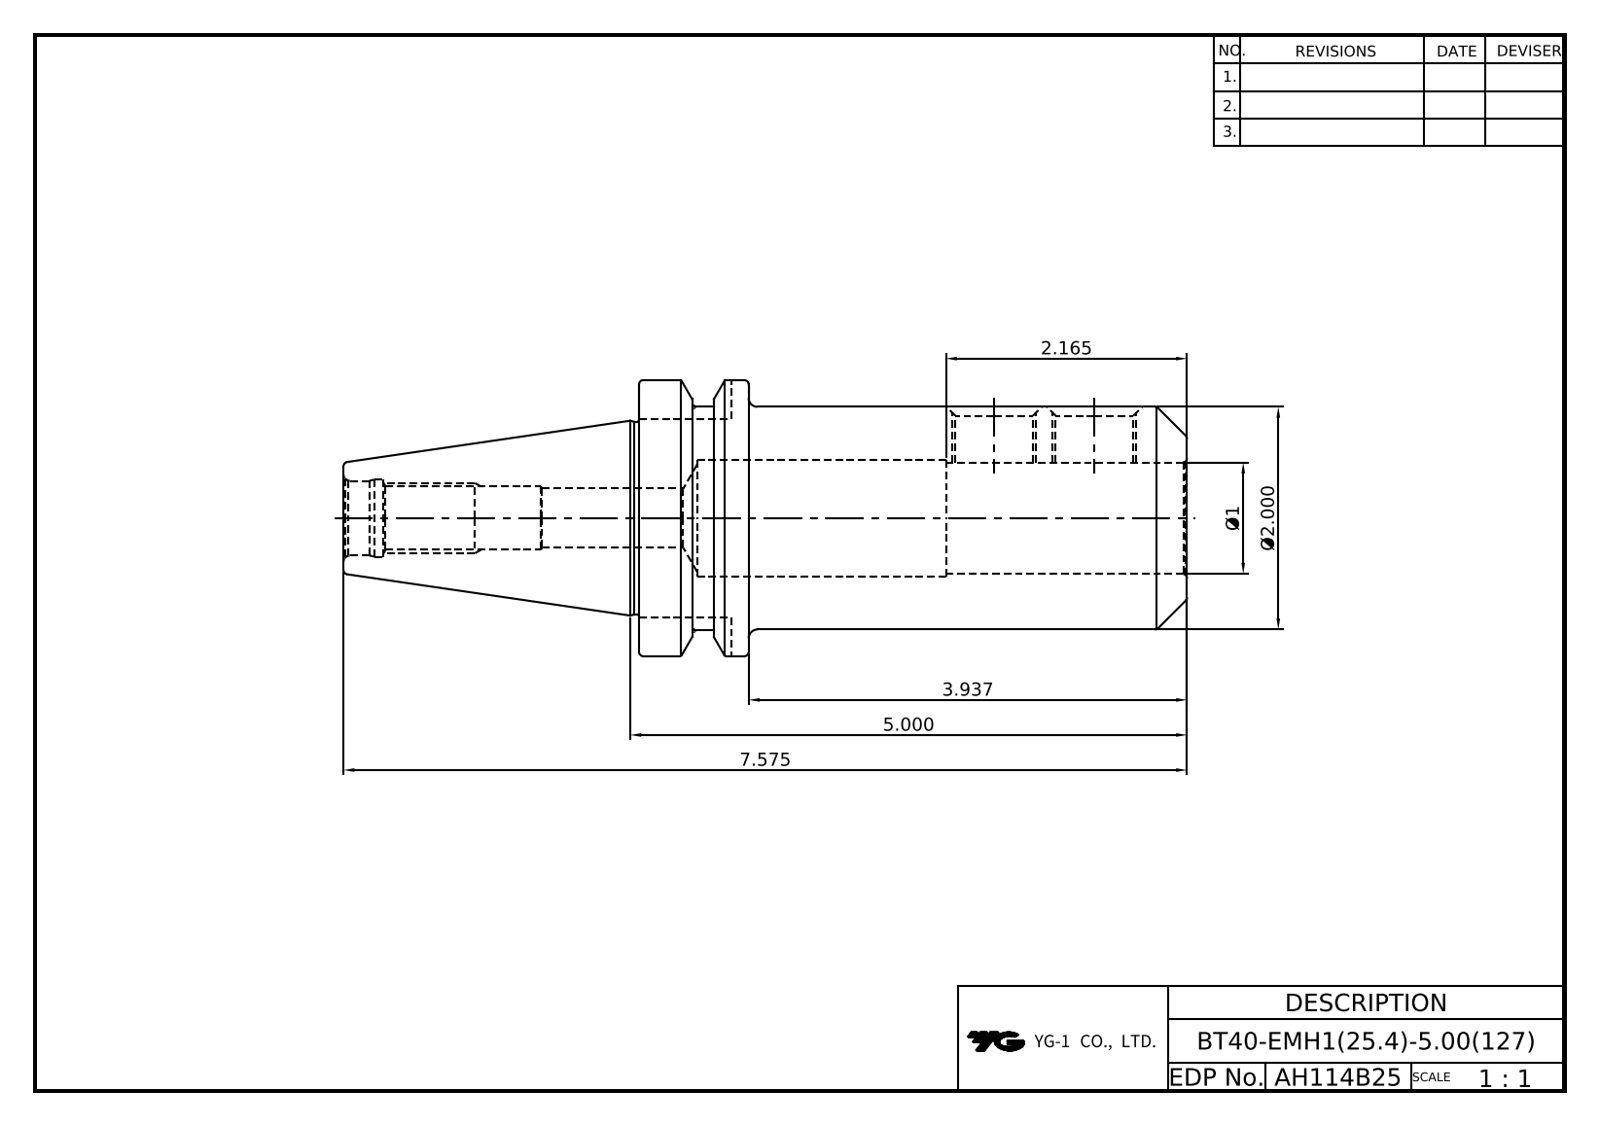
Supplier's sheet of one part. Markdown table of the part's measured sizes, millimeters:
| quantity | value |
| --- | --- |
| part name | LO-BT40-EMH25.4-127 |
| STEP written by | Autodesk Inventor 2022 (AUTOMOTIVE_DESIGN) |
| units | millimeters |
| bodies | 1 solid, 56 faces (17 planar, 17 cylindrical, 22 other) |
| overall size | 192.4 × 63 × 63 |
| volume | 254 518 mm³ |
| surface area | 46 474 mm² |
| round holes (diameter × count) | 17.32 × 2, 13.5 × 1, 13.84 × 1, 17 × 1, 17.6 × 1, 25.4 × 1, 26.6 × 1 |
| round bosses / shafts (diameter × count) | 63 × 1, 52.6 × 1, 50.8 × 1, 44 × 1 |
| partial cylindrical surfaces (radius × count) | 8.05 × 1 |
| main face-to-face distances | 25, 125, 100, 45.2, 16.1, 67.4, 92.4, 192.4, 84.5, 17.1 |
| hole center spacings | 22.9 |
